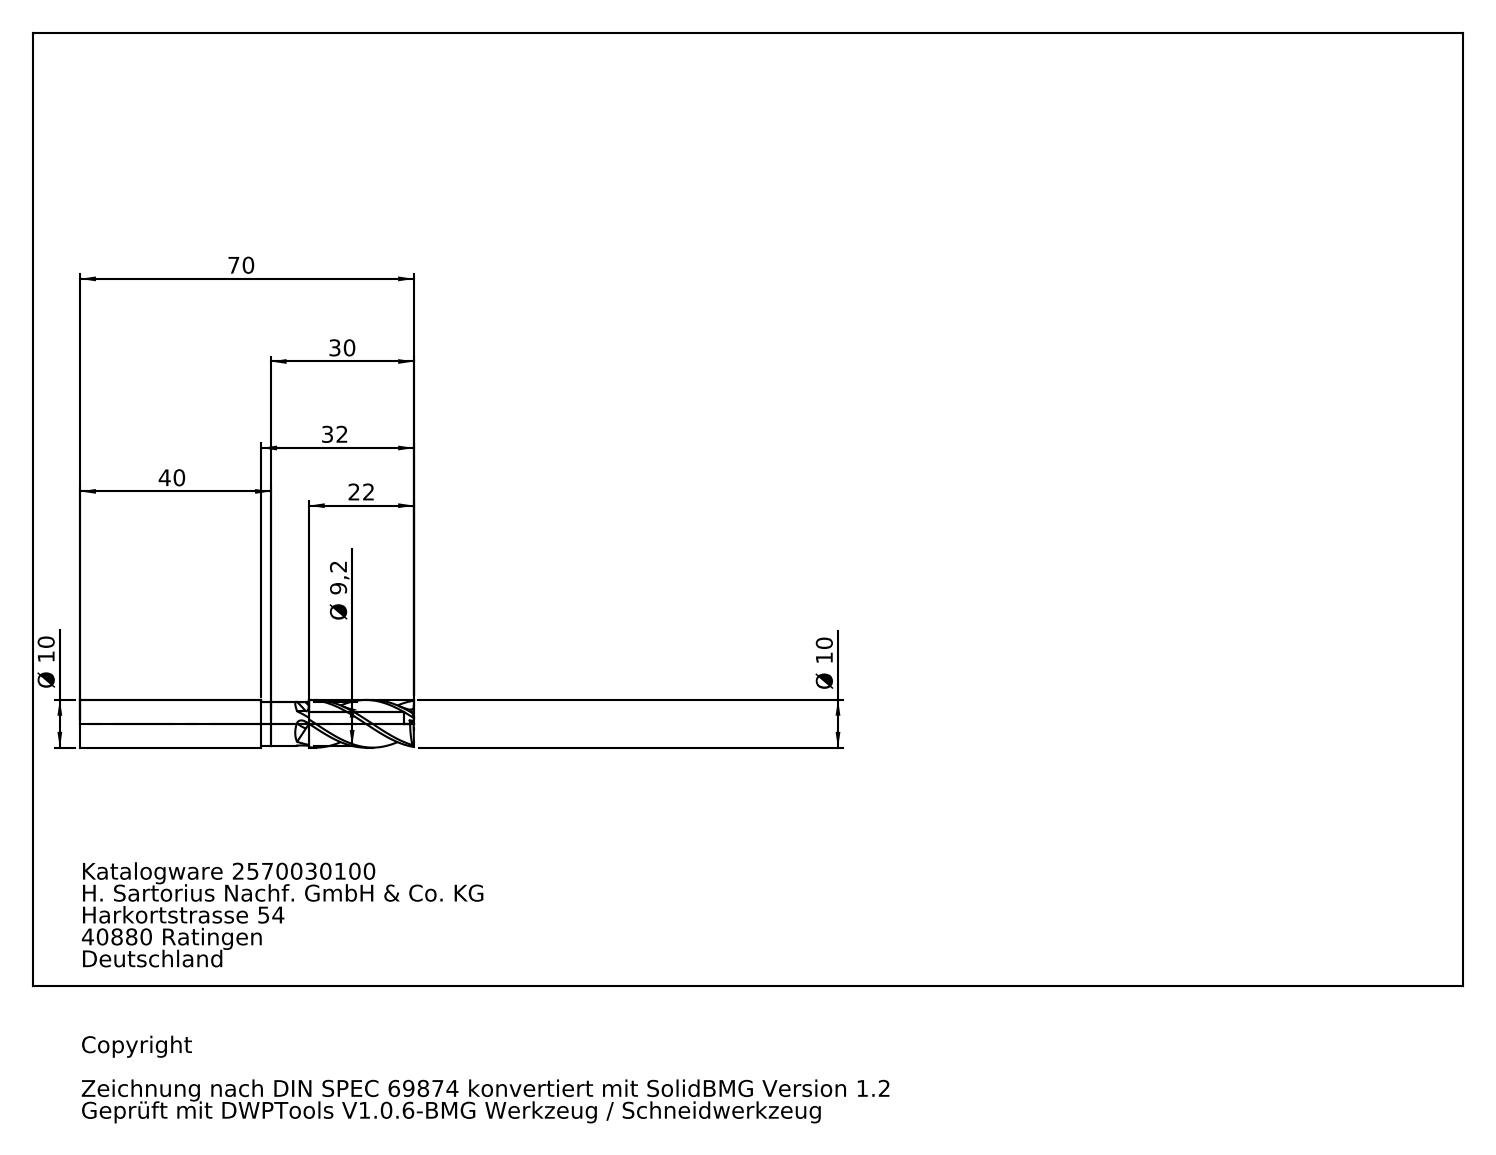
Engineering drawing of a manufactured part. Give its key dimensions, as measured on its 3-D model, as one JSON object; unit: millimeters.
{"part_name": "2570030100", "step_written_by": "SolidWorks 2010 (AUTOMOTIVE_DESIGN)", "units": "millimeters", "bodies": {"solids": 2, "faces": 59, "planar": 19, "cylindrical": 18, "other": 22}, "overall_size": [70, 10, 10], "volume_mm3": 4523, "surface_area_mm2": 3078, "round_holes": [[5, 1]], "round_bosses_or_shafts": [[10, 1], [9.2, 1]], "face_to_face_distances": [48, 67.89, 19.89, 38, 10, 29.89, 70, 32, 22, 2.11]}
